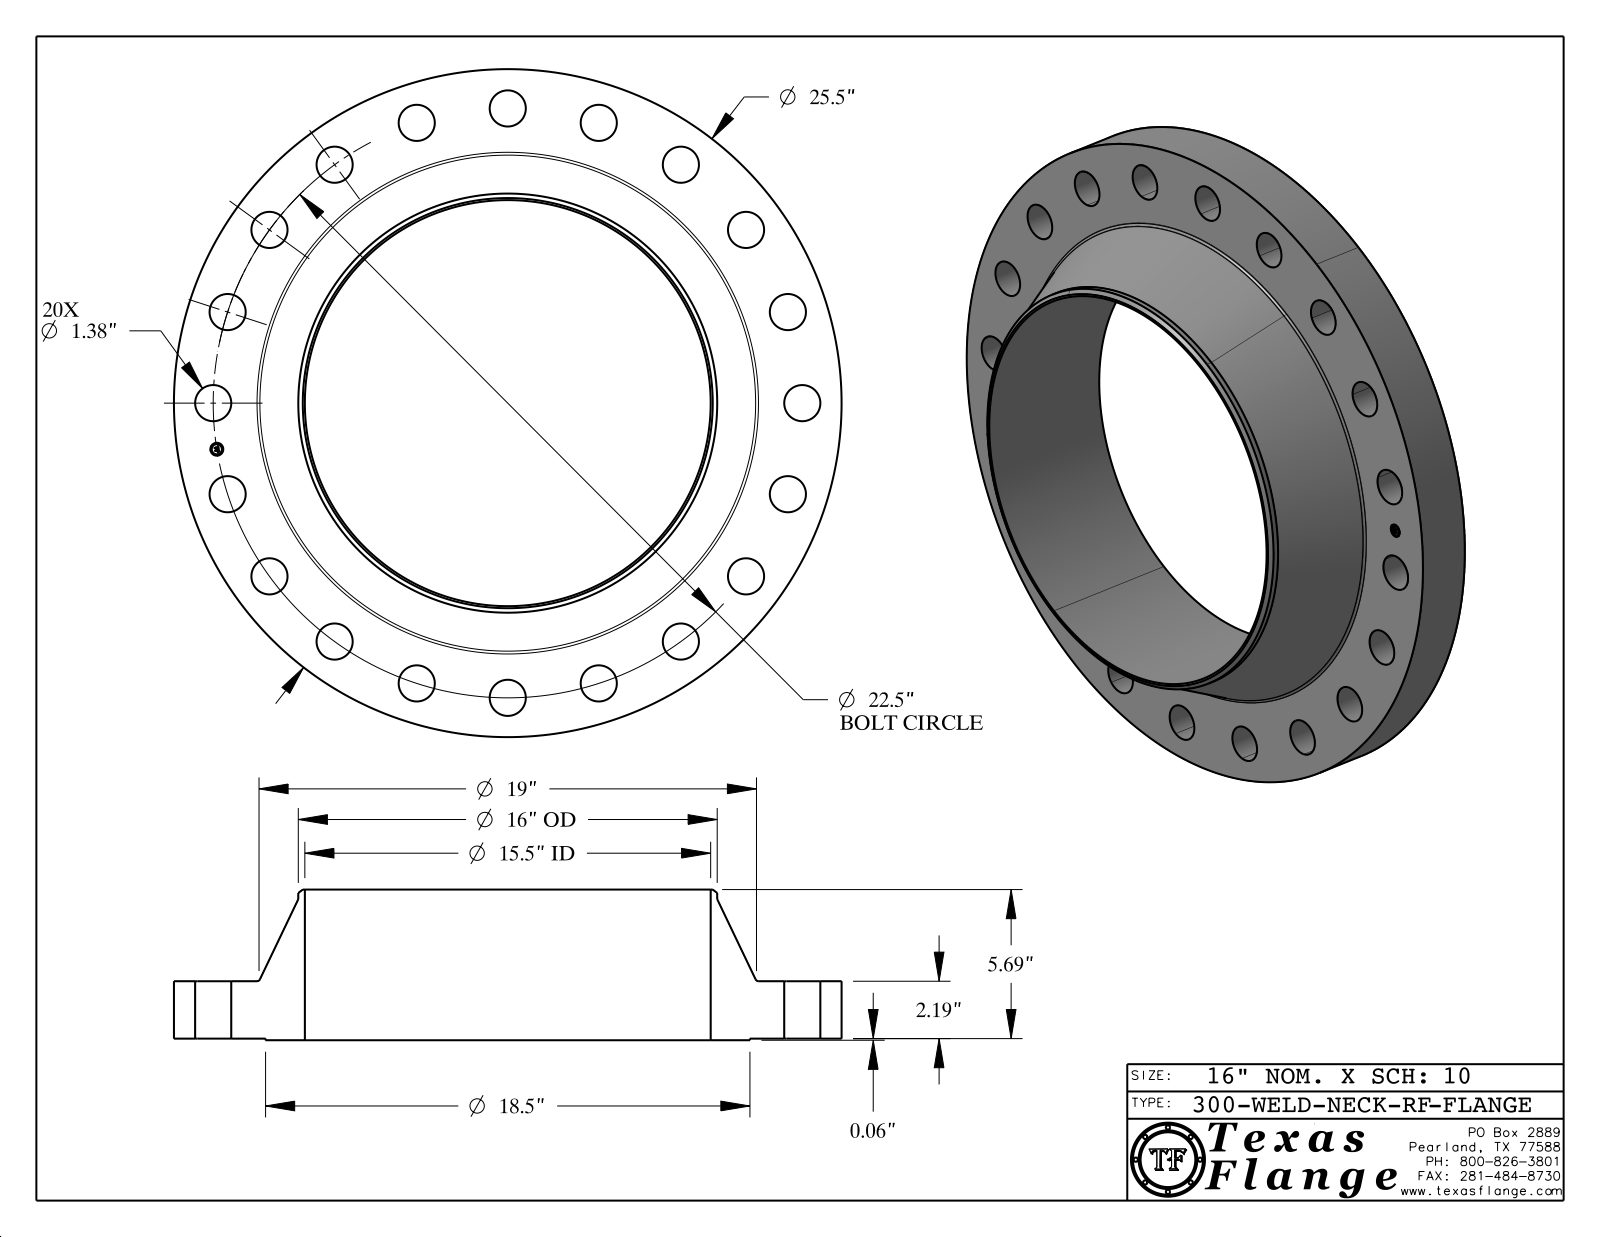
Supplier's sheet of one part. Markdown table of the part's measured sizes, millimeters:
| quantity | value |
| --- | --- |
| part name | 300-WELD-NECK-RF |
| STEP written by | CATIA V5 STEP AP214 (AUTOMOTIVE_DESIGN) |
| units | millimeters |
| bodies | 1 solid, 443 faces (369 planar, 68 cylindrical, 6 other) |
| overall size | 647.7 × 647.7 × 146.1 |
| volume | 13 320 000 mm³ |
| surface area | 874 200 mm² |
| round holes (diameter × count) | 35.1 × 20, 12.6 × 1, 393.7 × 1 |
| round bosses / shafts (diameter × count) | 0.8 × 8, 647.7 × 1, 469.9 × 1, 406.4 × 1, 9.9 × 1 |
| main face-to-face distances | 55.6, 1.6, 57.2, 146.1, 144.5, 88.9, 56.8, 55.2, 0.4, 89.3 |
| hole center spacings | 285.8, 176.6, 335.9, 89.4, 462.4, 509.2, 543.5, 564.5 |
